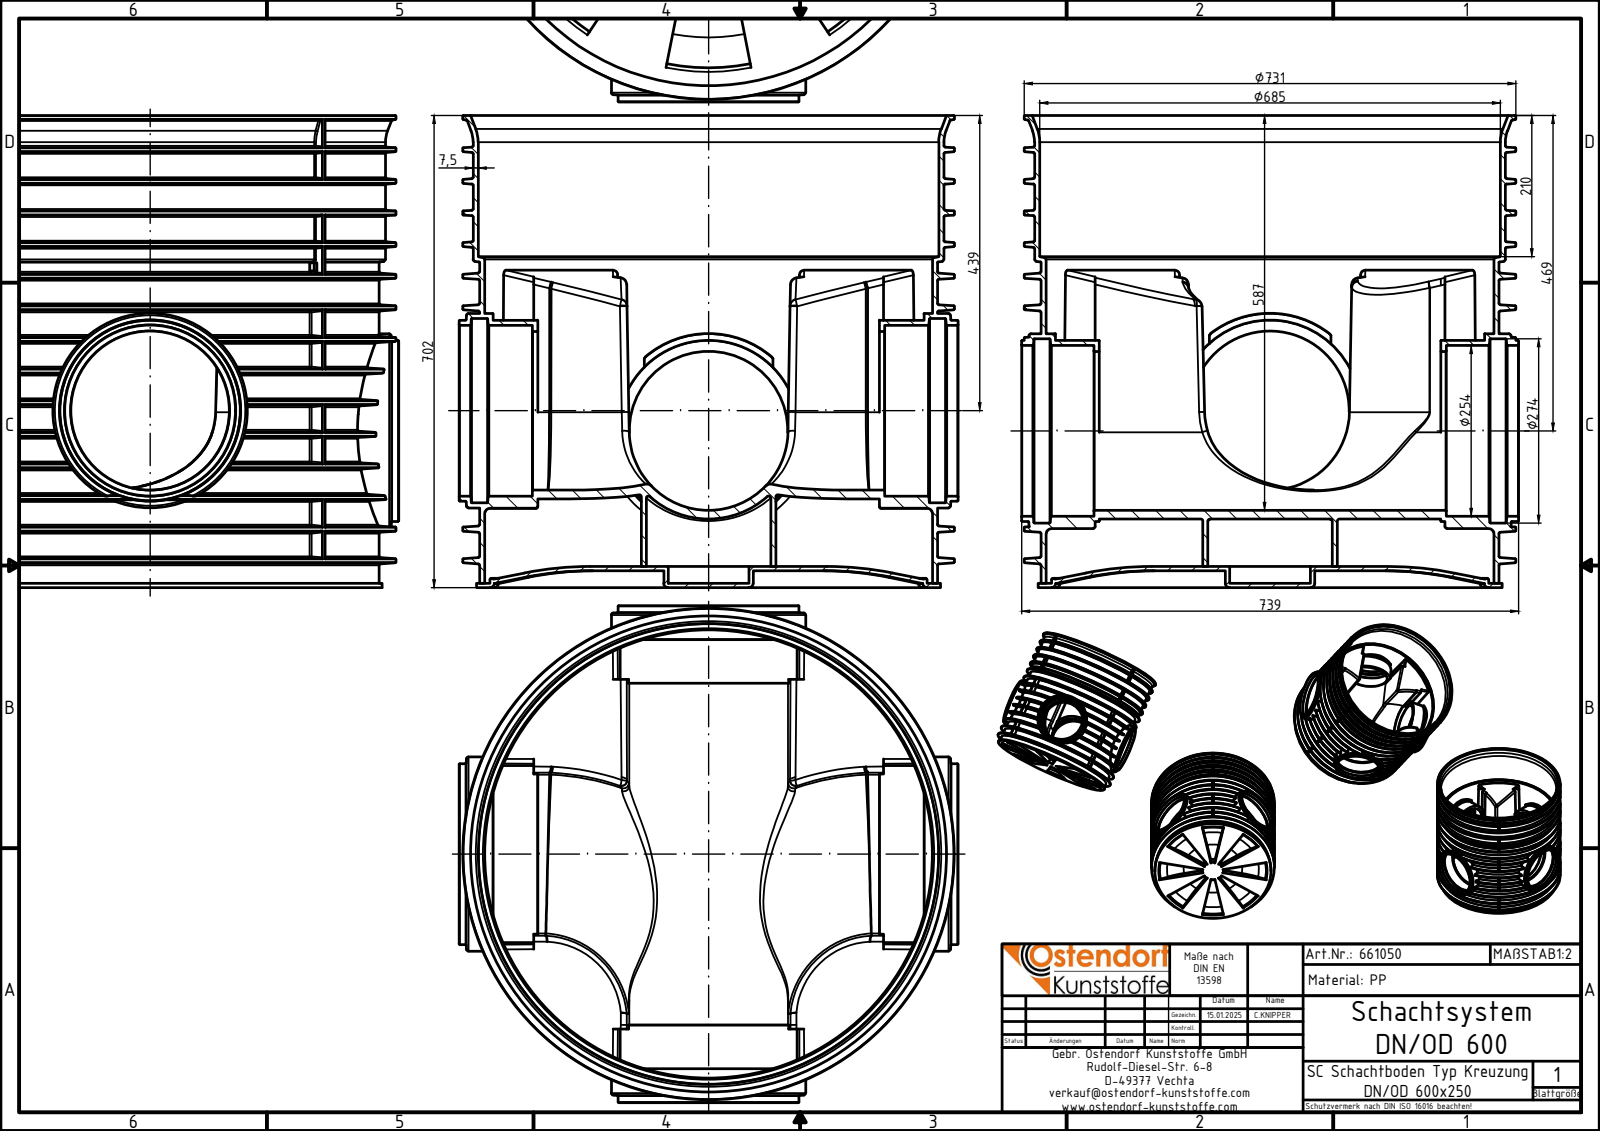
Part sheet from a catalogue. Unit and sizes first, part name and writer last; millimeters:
Units: millimetres
Overall size (bounding box): 742 × 739 × 702
Round holes (diameter × count): ⌀236 ×2, ⌀254 ×2, ⌀274 ×2, ⌀120 ×1, ⌀185 ×1, ⌀640 ×1, ⌀666 ×1, ⌀685 ×1
Round bosses / shafts (diameter × count): ⌀289 ×2, ⌀269 ×2, ⌀731 ×1, ⌀700 ×1, ⌀690 ×1, ⌀681 ×1, ⌀650 ×1, ⌀200 ×1
Partial cylindrical surfaces — rounded edges, fillets, slot ends (radius × count): R2 ×16, R1 ×8, R3 ×8, R131 ×4, R118 ×2, R145.1 ×2, R66.5 ×1, R140.5 ×1
Main face-to-face distances: 6.5, 25, 31.5, 13, 18.5, 14.1, 8, 516, 702, 695.5
Volume: 32 470 000 mm³ · Surface area: 6 675 000 mm²
Bodies: 2 solids, 1963 faces (222 planar, 366 cylindrical, 1375 other)
Part name (STEP PRODUCT): 661050z; 661050 Schacht DN600 Boden; 661050 Schachtboden DN600 Grundkörper
STEP written by: Autodesk Inventor 2024 (AUTOMOTIVE_DESIGN)
